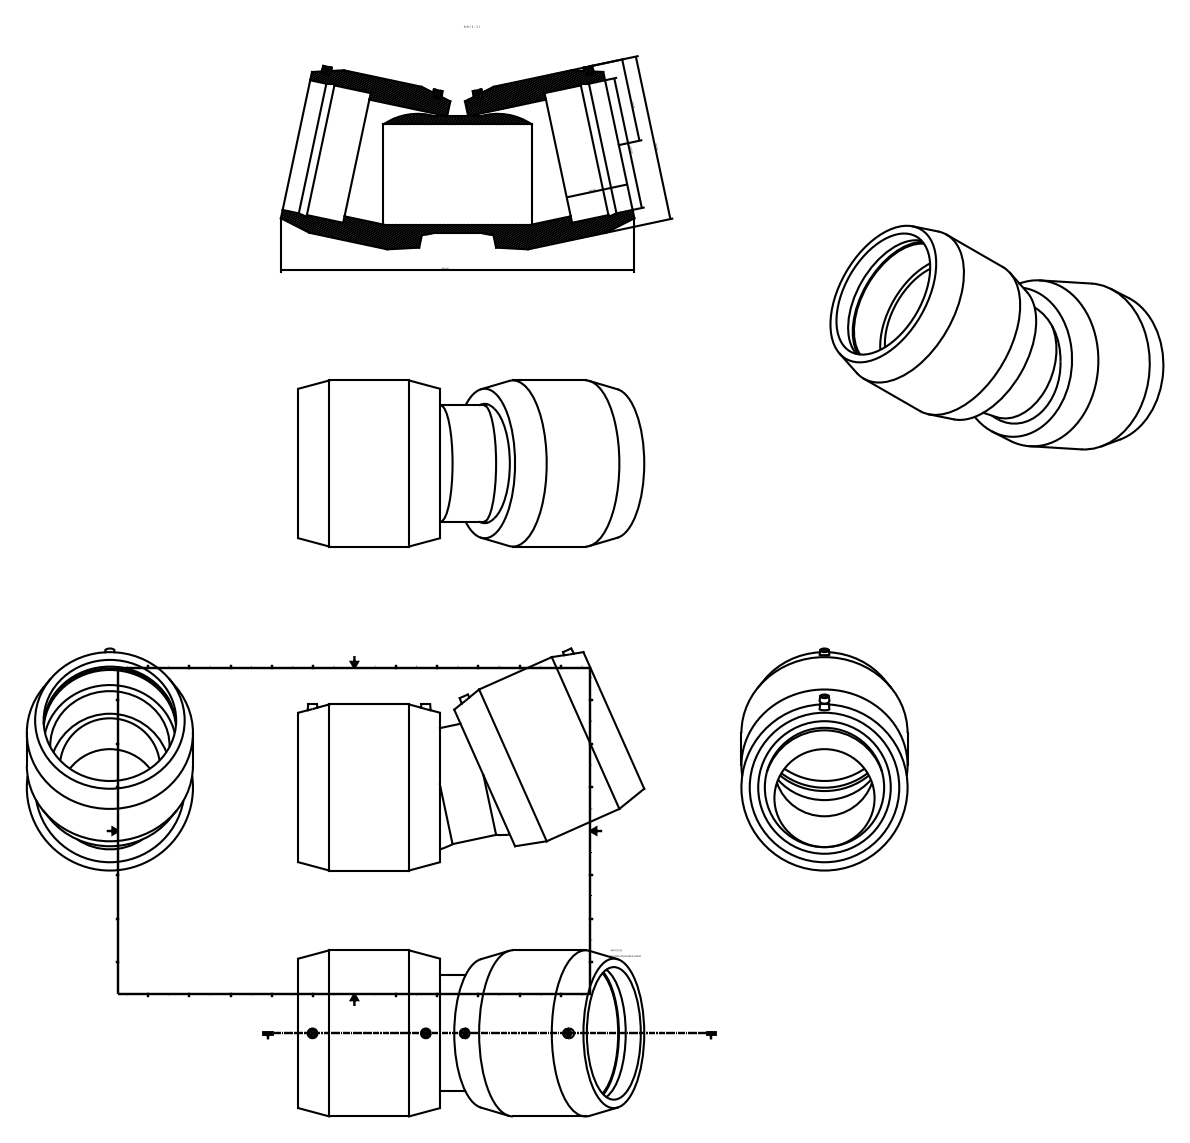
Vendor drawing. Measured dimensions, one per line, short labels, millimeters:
name: 4947C4225
written by: Autodesk Inventor 2015 (AUTOMOTIVE_DESIGN)
unit: mm
bodies: 1 solid, 50 faces (20 planar, 18 cylindrical, 12 other)
size: 586.89 × 376.88 × 282
volume: 13 480 000 mm³; area: 1 036 000 mm²
holes: 4× ⌀10, 3× ⌀225, 2× ⌀202.5, 1× ⌀170.01
bosses: 4× ⌀4, 2× ⌀282, 1× ⌀197.01
face distances: 240, 240.12, 105, 135, 135.07, 105.05, 42, 63, 198, 198.1
hole spacings: 192
